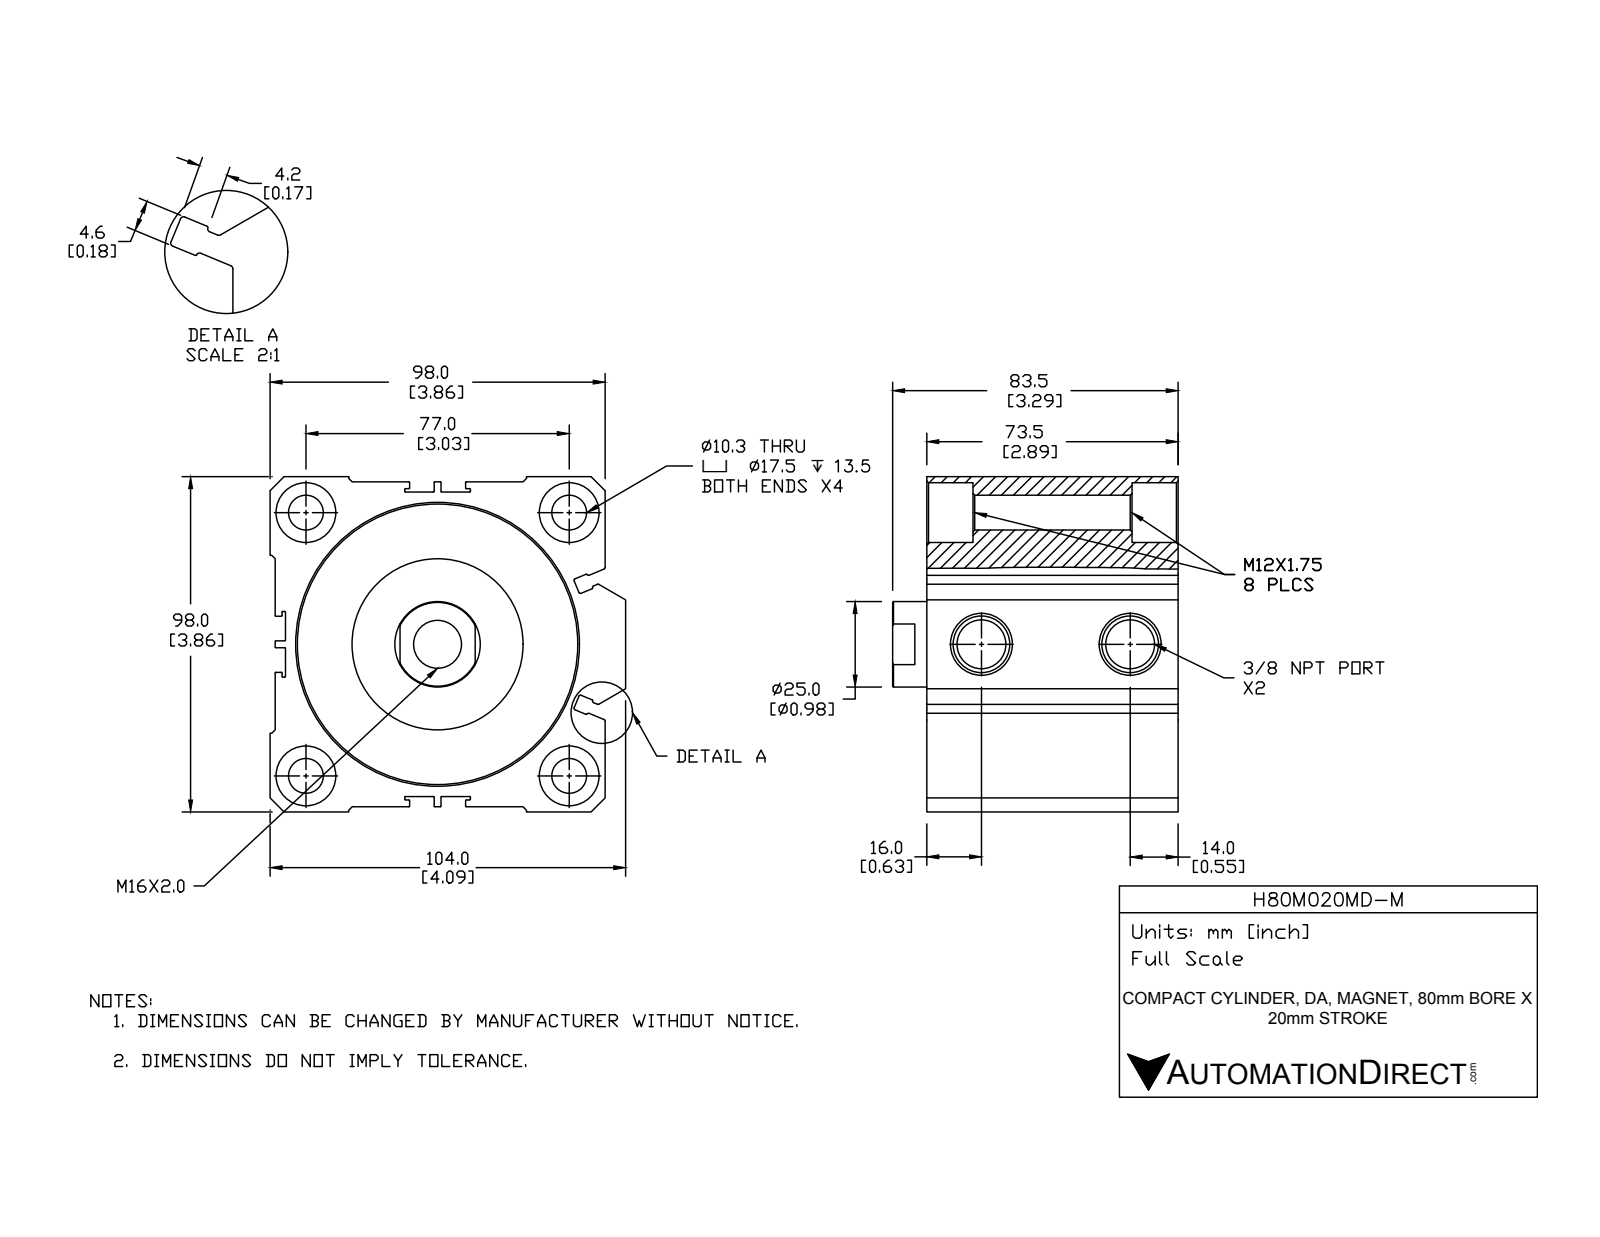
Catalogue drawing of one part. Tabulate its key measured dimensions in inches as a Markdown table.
| quantity | value |
| --- | --- |
| part name | H80M020MD-M-BODY; H80M020MD-M-PISTON; H80M020MD-M |
| STEP written by | SolidWorks 2015 (CONFIG_CONTROL_DESIGN) |
| units | inches |
| bodies | 2 solids, 261 faces (105 planar, 103 cylindrical, 53 other) |
| overall size | 4.094 × 3.858 × 3.287 |
| volume | 31.46 in³ |
| surface area | 174.9 in² |
| round holes (diameter × count) | 0.402 × 4, 0.689 × 4, 0.562 × 2, 0.551 × 1, 0.984 × 1, 1.792 × 1, 3.15 × 1, 3.228 × 1 |
| round bosses / shafts (diameter × count) | 1.969 × 1, 1.535 × 1 |
| partial cylindrical surfaces (radius × count) | 0.008 × 40, 0.02 × 12 |
| main face-to-face distances | 3.799, 0.059, 3.858, 0.354, 1.421, 1.067, 2.209, 1.854, 0.787, 0.079 |
| hole center spacings | 2.144, 3.031, 4.287, 1.713 |
